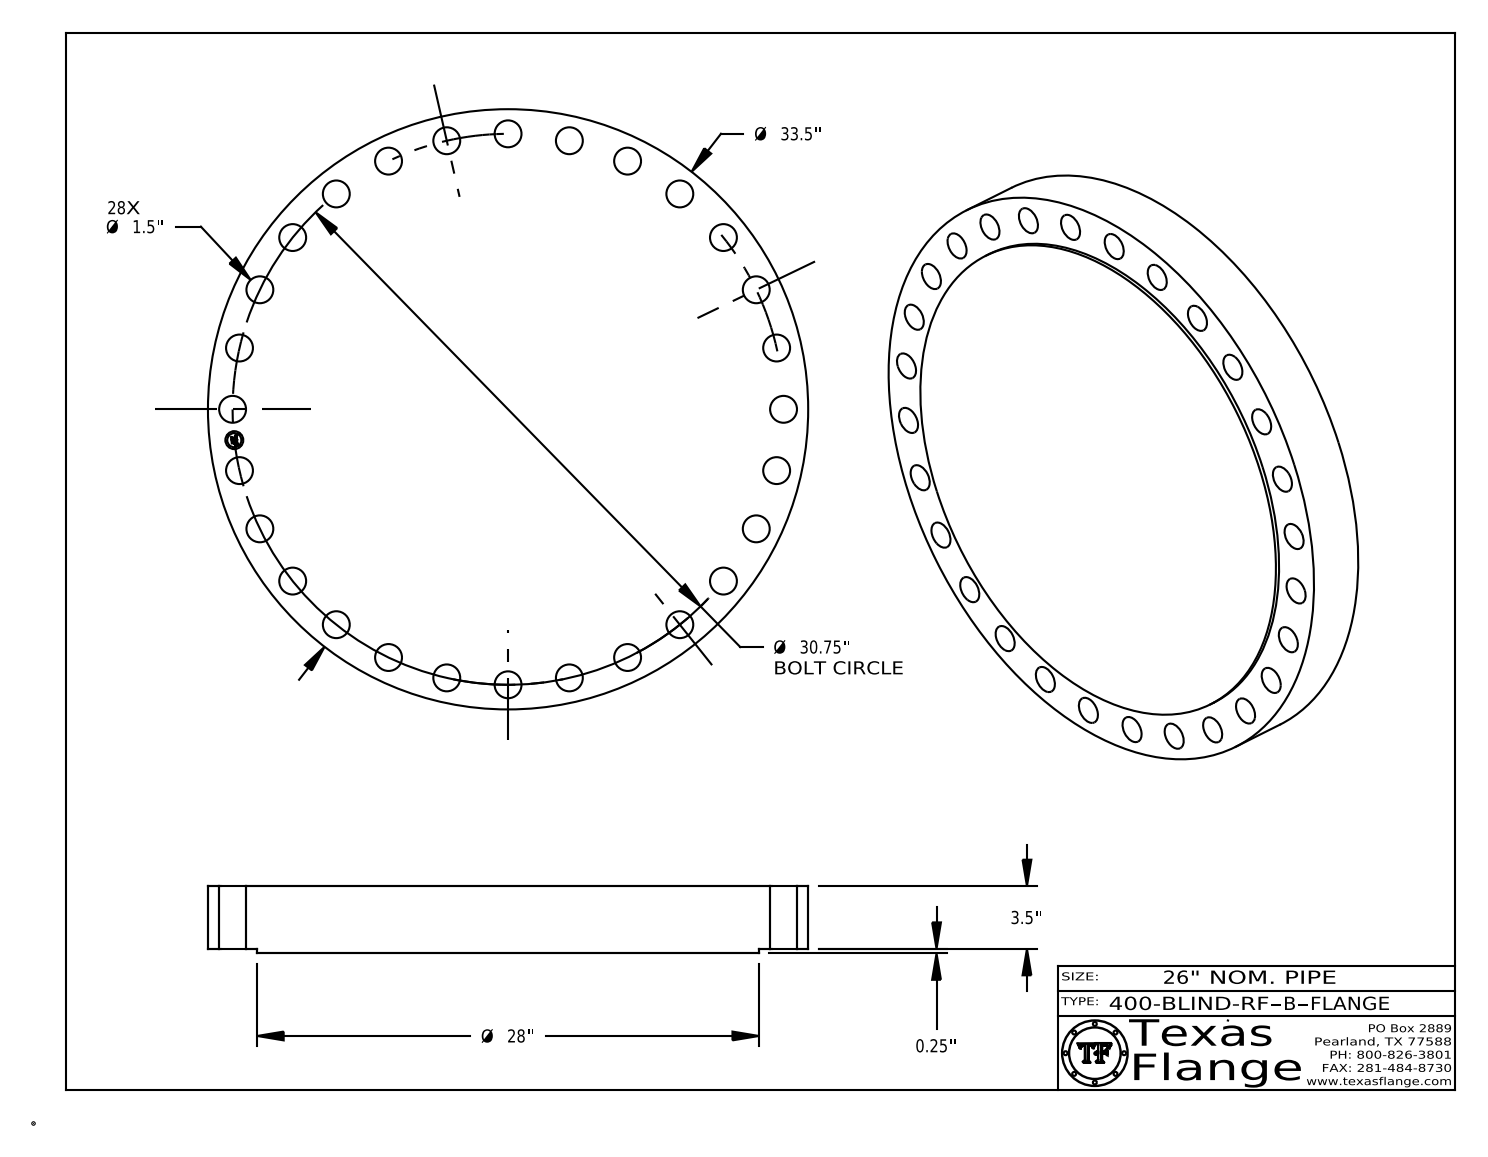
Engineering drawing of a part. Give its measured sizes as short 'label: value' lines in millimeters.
name: 400-BLIND-RF, Series B
written by: CATIA V5 STEP AP214 (AUTOMOTIVE_DESIGN)
unit: mm
bodies: 1 solid, 448 faces (368 planar, 80 cylindrical, 0 other)
size: 850.9 × 850.9 × 95.3
volume: 50 240 000 mm³; area: 1 623 000 mm²
holes: 28× ⌀38.1, 1× ⌀25.4
bosses: 8× ⌀1.5, 1× ⌀850.9, 1× ⌀711.2, 1× ⌀20
face distances: 95.3, 6.4, 88.9, 94.9, 88.5, 0.4, 7.6, 7.4, 1.4, 4.9
hole spacings: 173.8, 737.2, 552.3, 338.9, 415.5, 487, 661.3, 761.5
